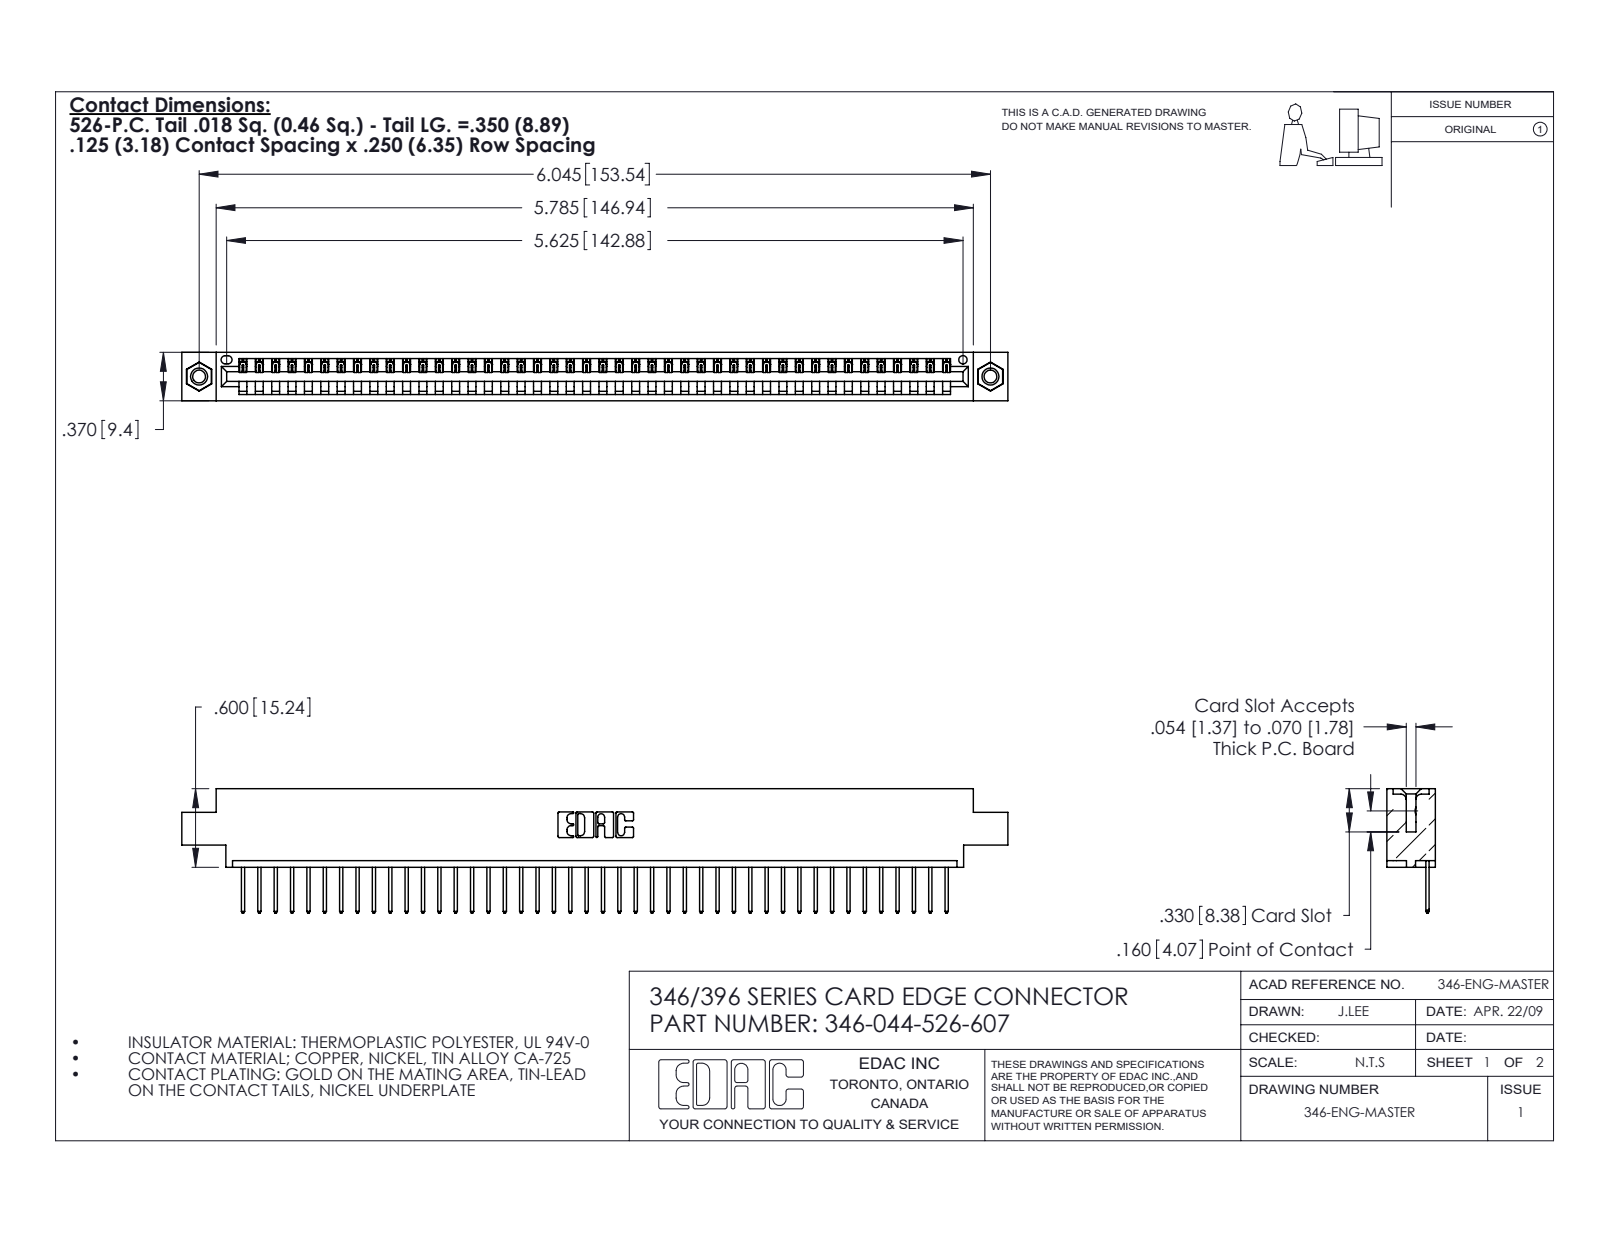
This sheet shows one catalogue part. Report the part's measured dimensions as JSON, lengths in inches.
{"part_name": "346-044-526-607; 345-250-001_345-250-005-103; 345-292-001_345-293-126; 346 Part_0.170 Offset - 0.156 Dia-TI", "step_written_by": "SolidWorks 2020 (CONFIG_CONTROL_DESIGN)", "units": "inches", "bodies": {"solids": 47, "faces": 2738, "planar": 1872, "cylindrical": 850, "other": 16}, "overall_size": [6.31, 0.95, 0.37], "volume_in3": 0.925, "surface_area_in2": 29.62, "round_holes": [[0.098, 2], [0.125, 2], [0.156, 2], [0.064, 1]], "round_bosses_or_shafts": [[0.155, 2]], "partial_cylinders_radius": [[0.006, 88], [0.01, 88], [0.01, 22], [0.007, 6], [0.031, 6], [0.026, 3], [0.031, 2], [0.04, 2]], "face_to_face_distances": [0.048, 0.322, 0.37, 0.25, 0.072, 0.298, 0.025, 0.222, 0.148, 0.1], "hole_center_spacings": [0.246, 5.836, 6.045]}
